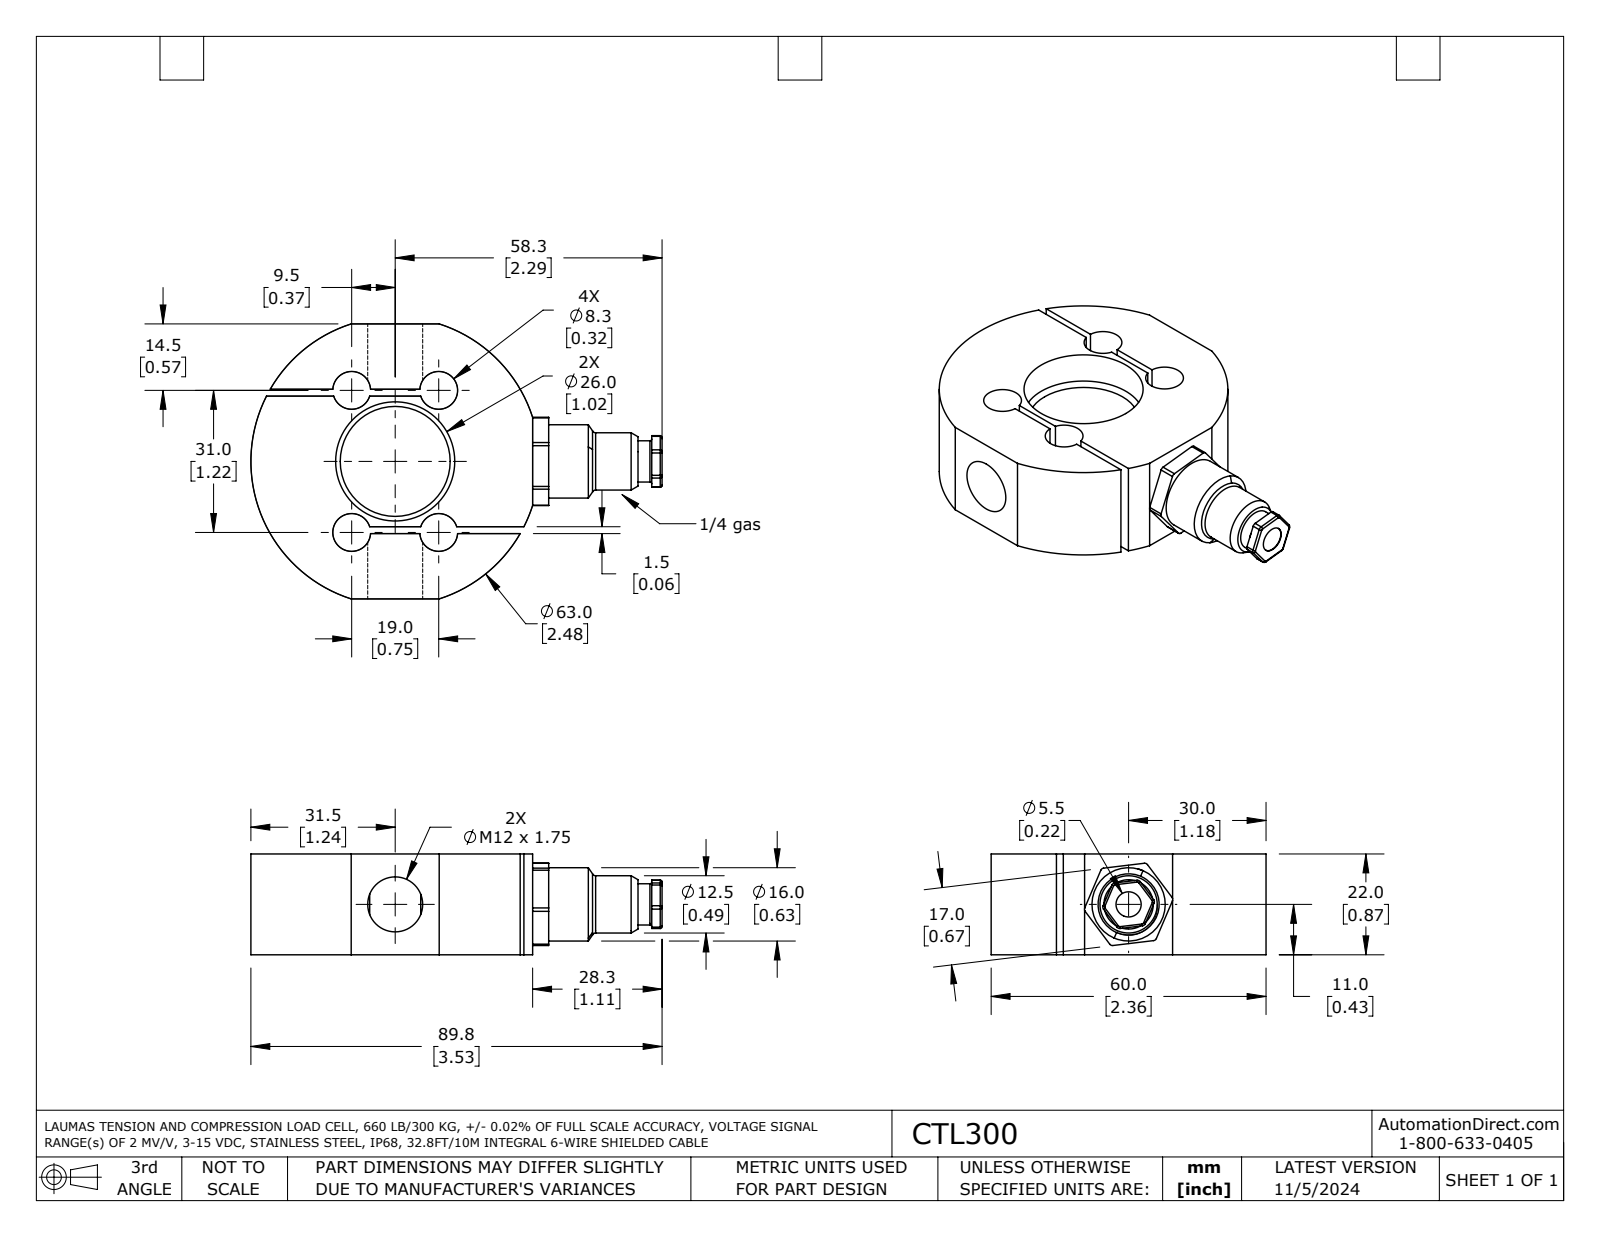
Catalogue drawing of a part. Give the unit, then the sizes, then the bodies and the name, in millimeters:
Units: millimetres
Overall size (bounding box): 89.7 × 60 × 22
Round holes (diameter × count): ⌀8.3 ×4, ⌀5.5 ×1, ⌀12 ×1, ⌀14 ×1, ⌀26 ×1
Round bosses / shafts (diameter × count): ⌀16 ×1, ⌀12.5 ×1, ⌀9 ×1
Partial cylindrical surfaces — rounded edges, fillets, slot ends (radius × count): R0.8 ×12, R0.4 ×6, R31.5 ×1
Main face-to-face distances: 22, 8, 14, 1.5, 30, 14.2, 15.7, 44.2, 45.7, 28.5
Hole centre spacings: 18.2, 19, 31, 36.3
Volume: 51 780 mm³ · Surface area: 18 170 mm²
Bodies: 2 solids, 114 faces (39 planar, 56 cylindrical, 19 other)
Part name (STEP PRODUCT): CTL300
STEP written by: SolidWorks 2021 (AUTOMOTIVE_DESIGN)
